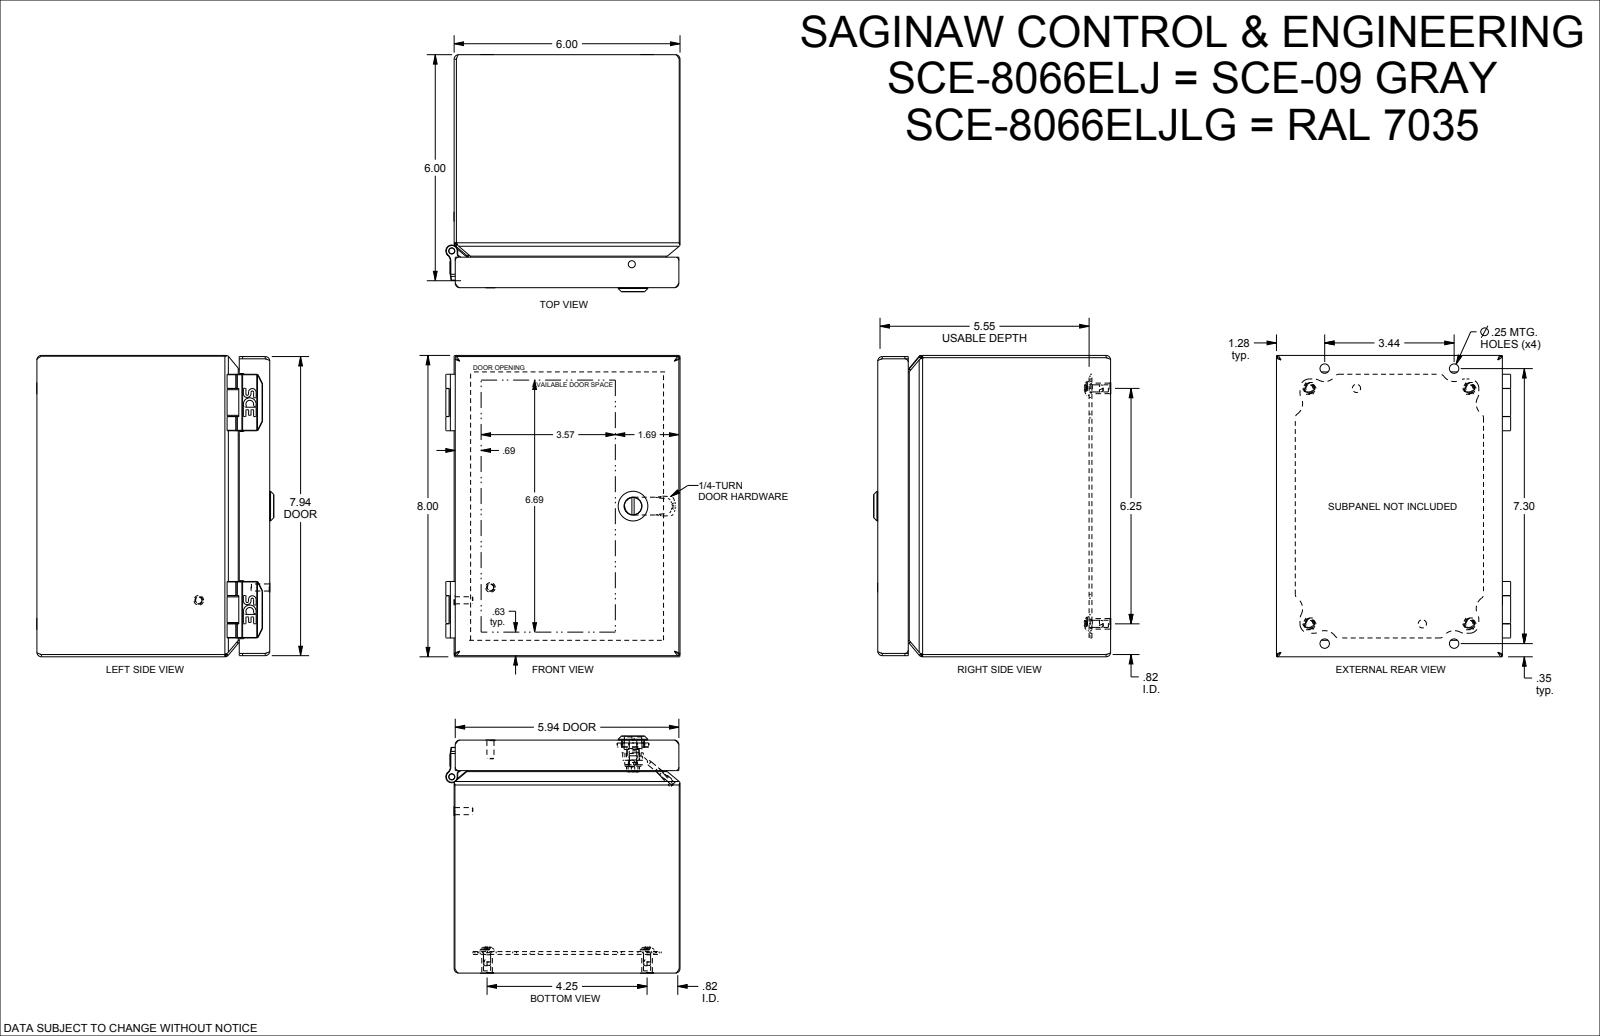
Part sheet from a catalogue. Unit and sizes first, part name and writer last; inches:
Units: inches
Overall size (bounding box): 8 × 6.296 × 6.22
Round holes (diameter × count): ⌀0.25 ×8, ⌀0.19 ×4, ⌀0.284 ×4, ⌀0.479 ×4, ⌀0.02 ×2, ⌀0.1 ×2, ⌀0.174 ×2, ⌀0.196 ×2, ⌀0.218 ×2, ⌀0.266 ×2, ⌀0.158 ×1, ⌀0.187 ×1
Round bosses / shafts (diameter × count): ⌀0.188 ×6, ⌀0.373 ×4, ⌀0.28 ×4, ⌀0.17 ×4, ⌀0.16 ×4, ⌀0.135 ×4, ⌀0.108 ×4, ⌀0.26 ×2
Partial cylindrical surfaces — rounded edges, fillets, slot ends (radius × count): R0.106 ×132, R0.005 ×131, R0.008 ×32, R0.01 ×26, R0.025 ×24, R0.03 ×24, R0.06 ×22, R0.013 ×21
Main face-to-face distances: 0.06, 5.94, 0.06, 7.94, 6.065, 6.124, 6.185, 6.125, 6, 5.88
Hole centre spacings: 0.663, 3.88, 6.787, 7.789, 0.994, 1.25, 2.646, 3
Bodies: 0 solids, 2654 faces (858 planar, 764 cylindrical, 1032 other)
Part name (STEP PRODUCT): SCE-8066ELJLG
STEP written by: SolidWorks 2019 (CONFIG_CONTROL_DESIGN)
